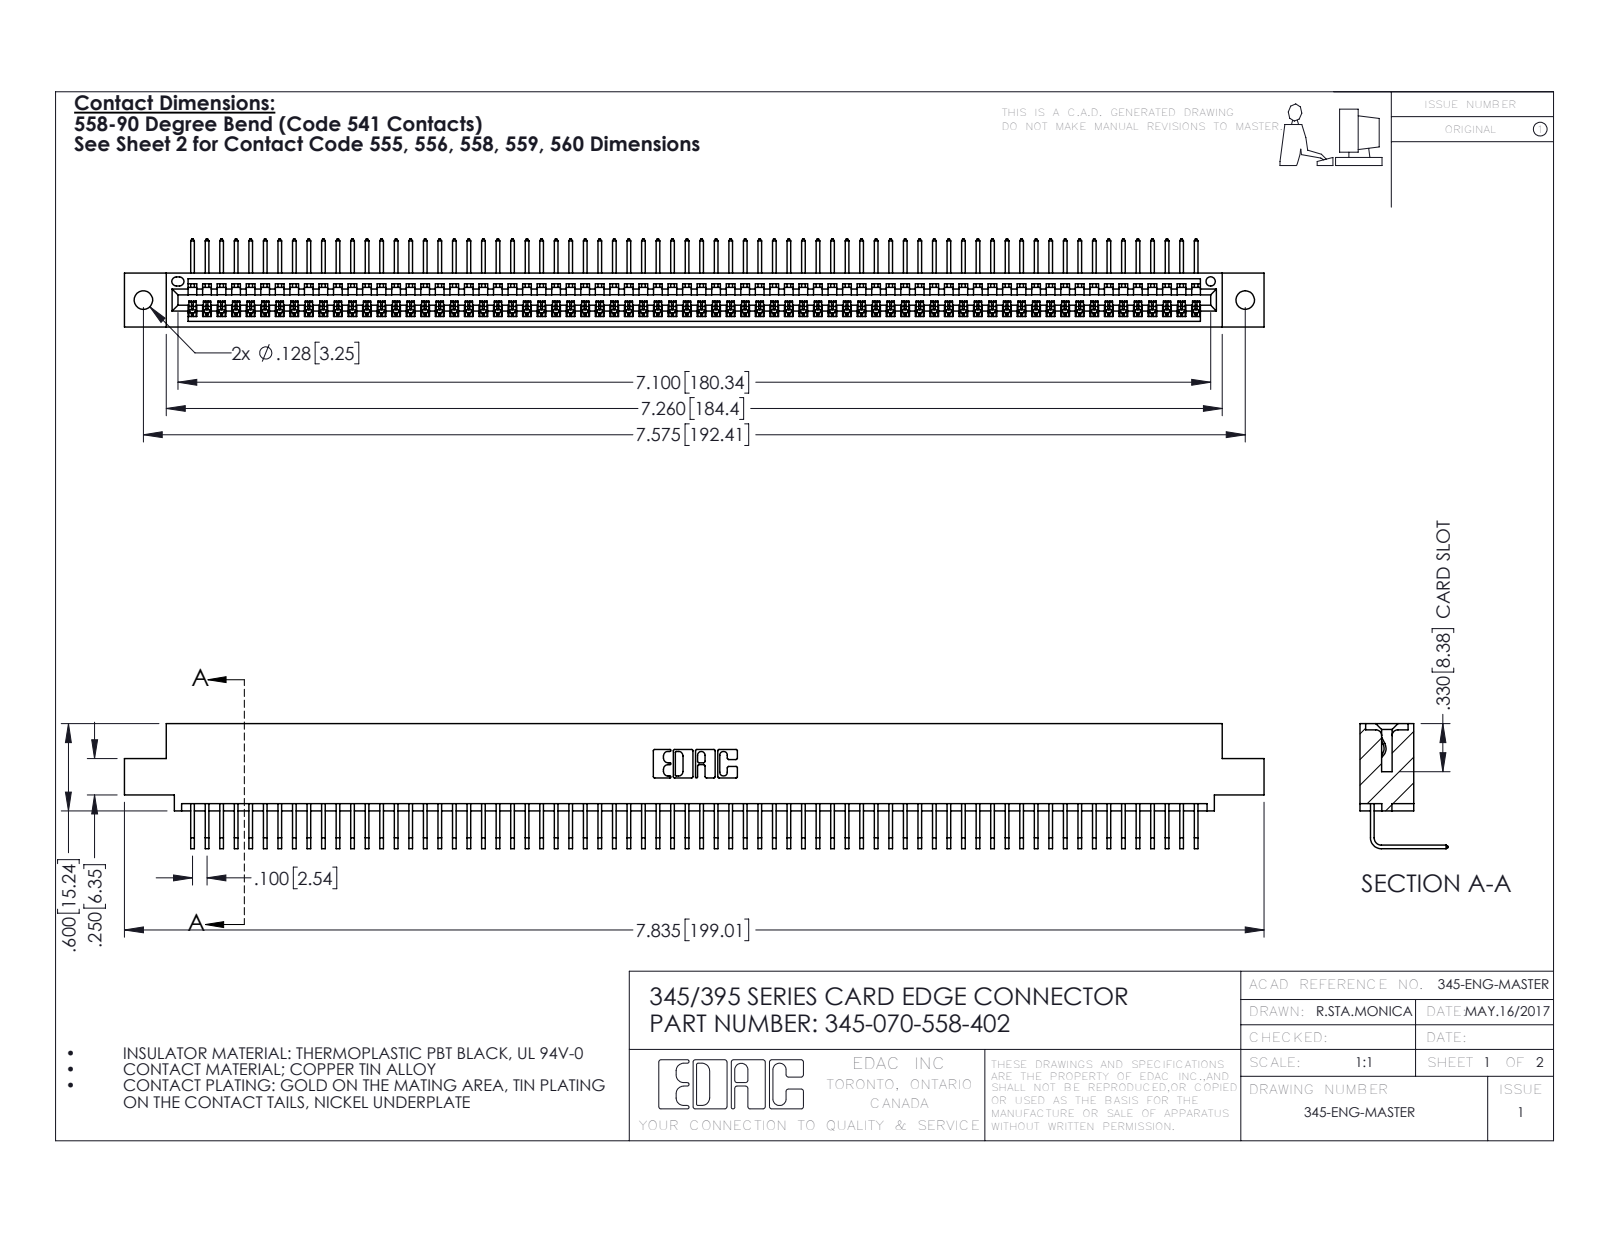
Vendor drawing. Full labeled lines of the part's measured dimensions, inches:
Part name (STEP PRODUCT): 345-292-001_558 Tail - 2; 345 Part_0.110 Offset - 0.128 Dia; 345-070-558-402
STEP written by: SolidWorks 2016 (CONFIG_CONTROL_DESIGN)
Units: inches
Bodies: 71 solids, 4330 faces (3024 planar, 1306 cylindrical, 0 other)
Overall size (bounding box): 7.835 × 0.859 × 0.605
Volume: 1.175 in³ · Surface area: 42.08 in²
Round holes (diameter × count): ⌀0.128 ×2, ⌀0.064 ×1
Partial cylindrical surfaces — rounded edges, fillets, slot ends (radius × count): R0.006 ×140, R0.01 ×22, R0.007 ×6, R0.031 ×6, R0.026 ×3, R0.031 ×2, R0.04 ×2, R0.014 ×1
Main face-to-face distances: 0.072, 0.298, 0.37, 0.2, 0.098, 0.272, 0.025, 0.225, 0.149, 0.072
Hole centre spacings: 0.27, 7.339, 7.575
